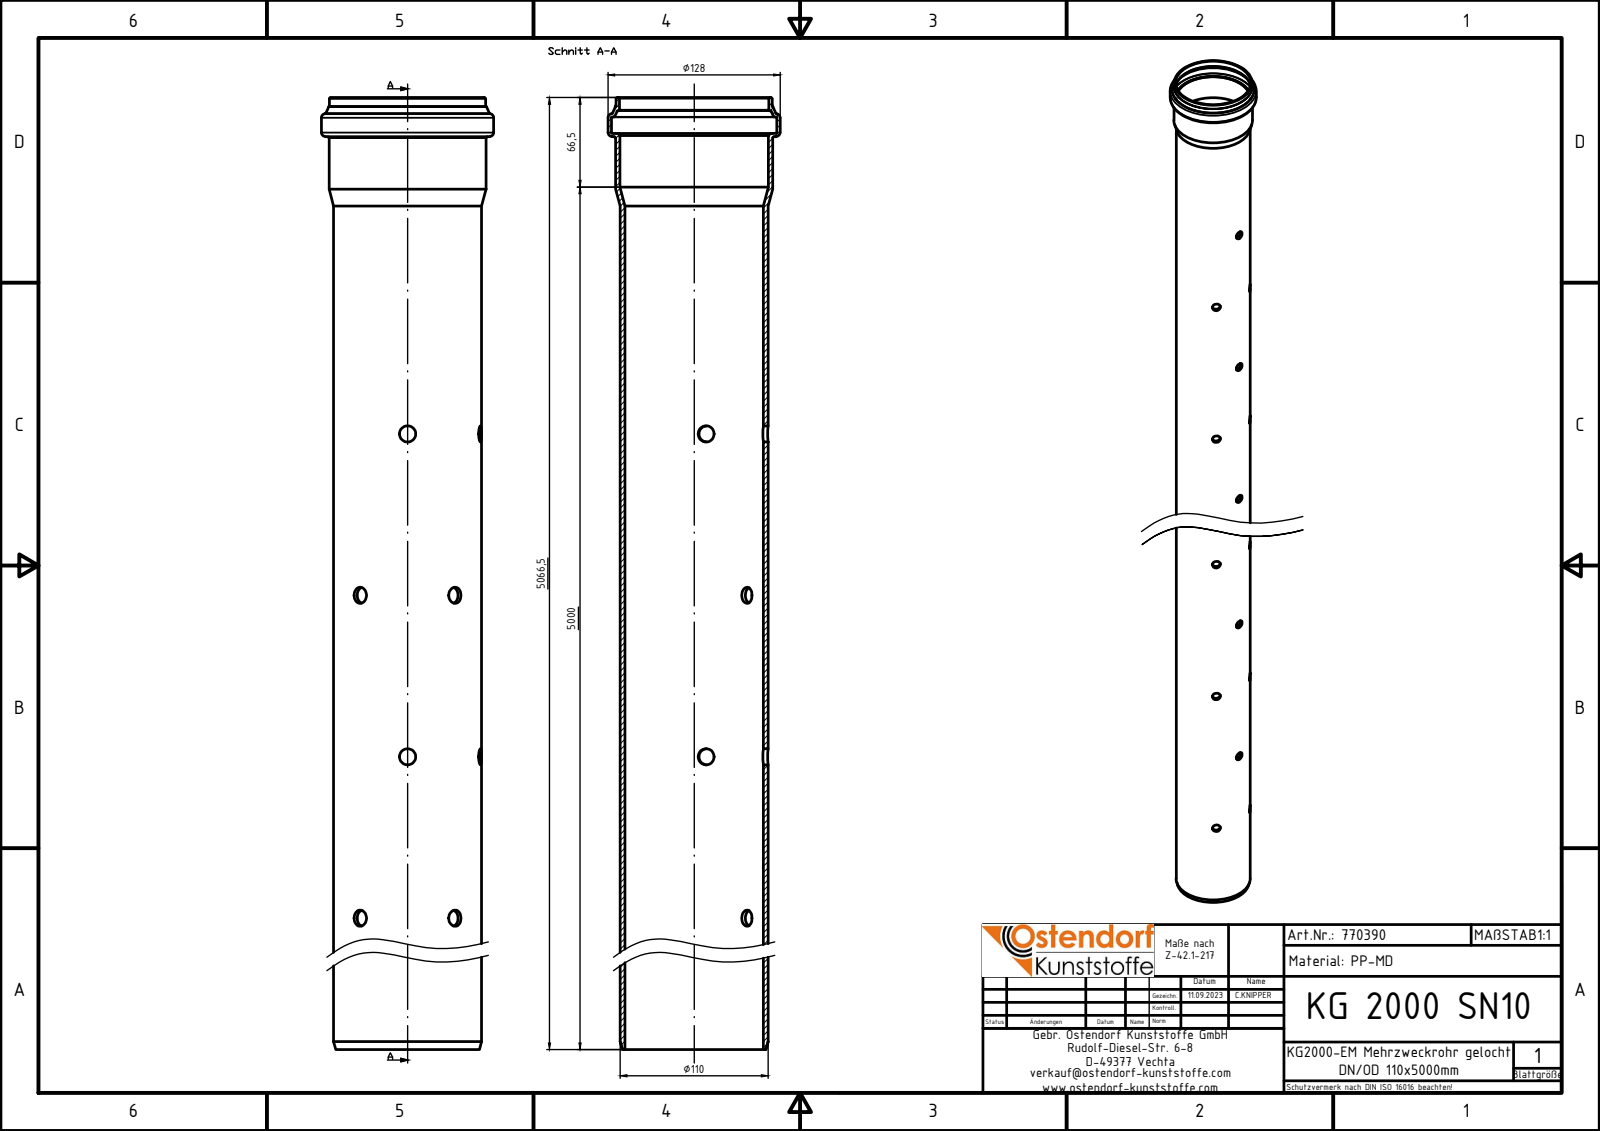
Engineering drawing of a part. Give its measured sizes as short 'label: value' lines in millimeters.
name: 770390z
written by: Autodesk Inventor 2024 (AUTOMOTIVE_DESIGN)
unit: mm
bodies: 1 solid, 116 faces (5 planar, 89 cylindrical, 22 other)
size: 5066.5 × 128 × 128
volume: 5 932 000 mm³; area: 3 394 000 mm²
holes: 80× ⌀12, 1× ⌀102.96, 1× ⌀110.5, 1× ⌀110.9, 1× ⌀122.8
bosses: 1× ⌀128, 1× ⌀116.7, 1× ⌀116.1, 1× ⌀110
face distances: 5037.4, 5066.5, 29.1, 5038.22, 0.82, 28.28, 5059.85, 22.45, 21.63, 6.65
hole spacings: 240, 480, 720, 960, 1200, 1440, 1680, 1920
